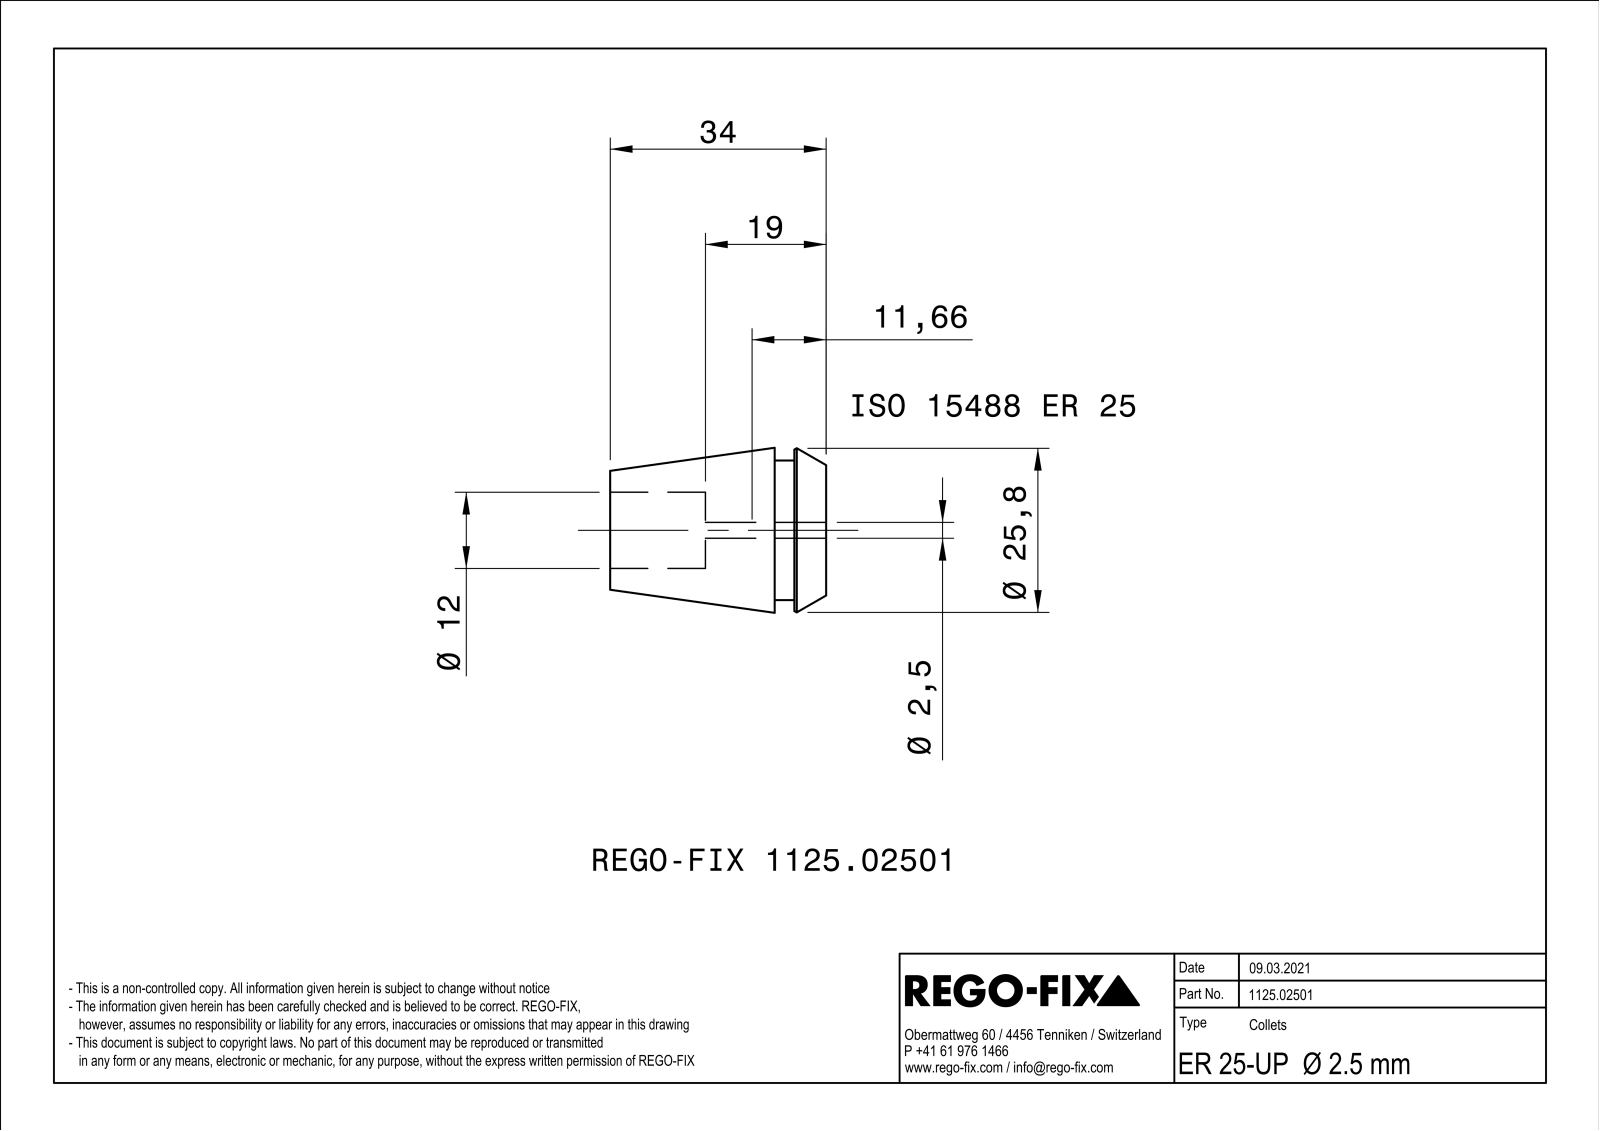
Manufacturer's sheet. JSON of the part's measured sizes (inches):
{"part_name": "NOCUT", "step_written_by": "SIEMENS PLM Software Solid Edge ST10 (AUTOMOTIVE_DESIGN)", "units": "inches", "bodies": {"solids": 1, "faces": 352, "planar": 152, "cylindrical": 80, "other": 120}, "overall_size": [1.339, 1.023, 1.023], "volume_in3": 0.575, "surface_area_in2": 14.71, "round_holes": [[0.472, 1]], "round_bosses_or_shafts": [[0.866, 1]], "partial_cylinders_radius": [[1.378, 8], [1.575, 8], [0.049, 1]], "face_to_face_distances": [0.031, 0.032, 0.031, 0.024, 0.197, 1.142, 0.025, 0.319, 1.339, 1.02]}
